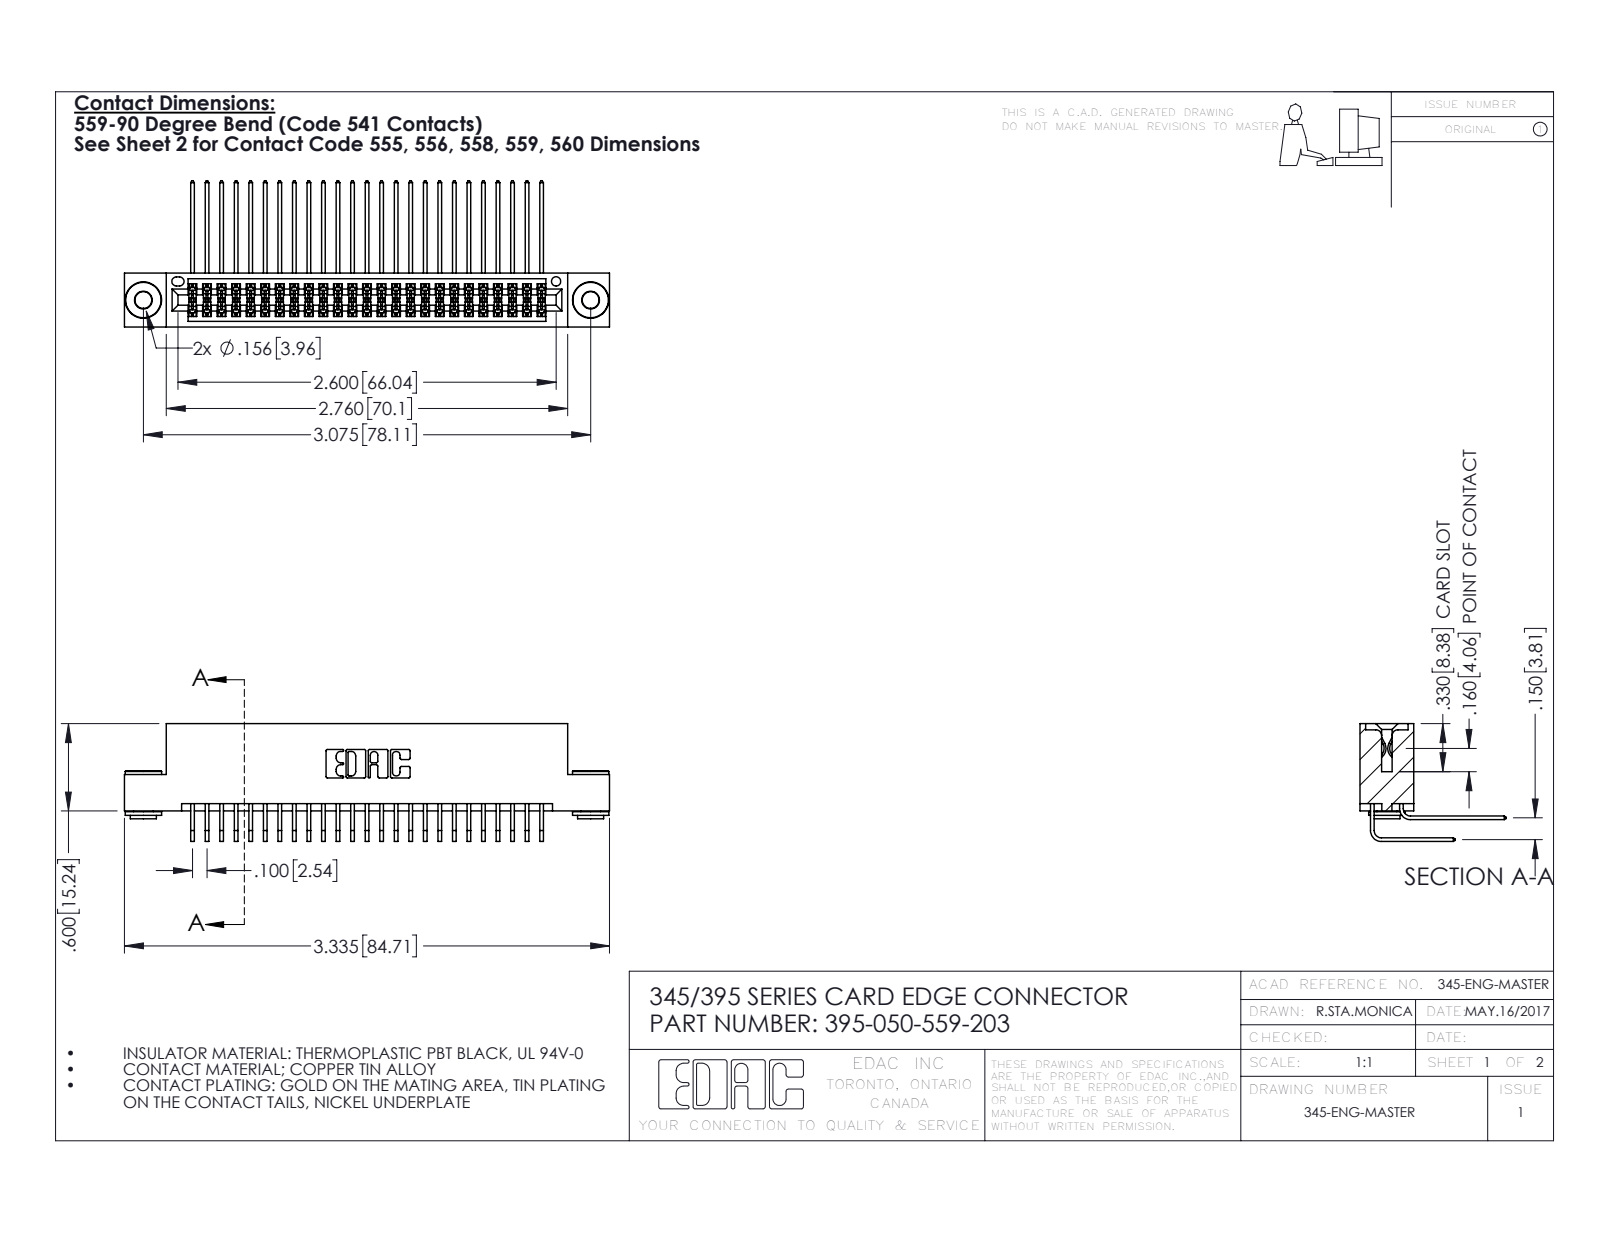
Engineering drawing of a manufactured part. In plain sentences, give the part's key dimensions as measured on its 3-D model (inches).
The part is named "345-292-001_559 Tail - 2; 345 Part_Flush Mounting Lugs - 0.156 Dia-TH; 345-250-002_345-250-002-102; 345-292-001_558 559 Tail - 1 (+1 more)". Its 3-D file was written by "SolidWorks 2016 (CONFIG_CONTROL_DESIGN)". It is 53 solids with 2764 faces: 1840 planar, 916 cylindrical and 8 other. Overall it measures 3.335 by 1.005 by 0.809 inches. Its volume is 0.511 cubic inches and its surface area 21.11 square inches. Round holes: 2 of diameter 0.116, 2 of diameter 0.156, 1 of diameter 0.064. Round bosses or shafts: 2 of diameter 0.25, 2 of diameter 0.18, 2 of diameter 0.136. Partial cylindrical surfaces (rounded edges, fillets, slot ends): 75 of radius 0.006, 22 of radius 0.01, 6 of radius 0.007, 6 of radius 0.031, 3 of radius 0.026, 2 of radius 0.014, 2 of radius 0.019, 2 of radius 0.022. The main face-to-face distances are 0.072, 0.298, 0.2, 0.37, 0.025, 0.098, 0.272, 0.225, 0.15, 0.175. The hole center spacings are 0.27, 2.84, 3.075.
